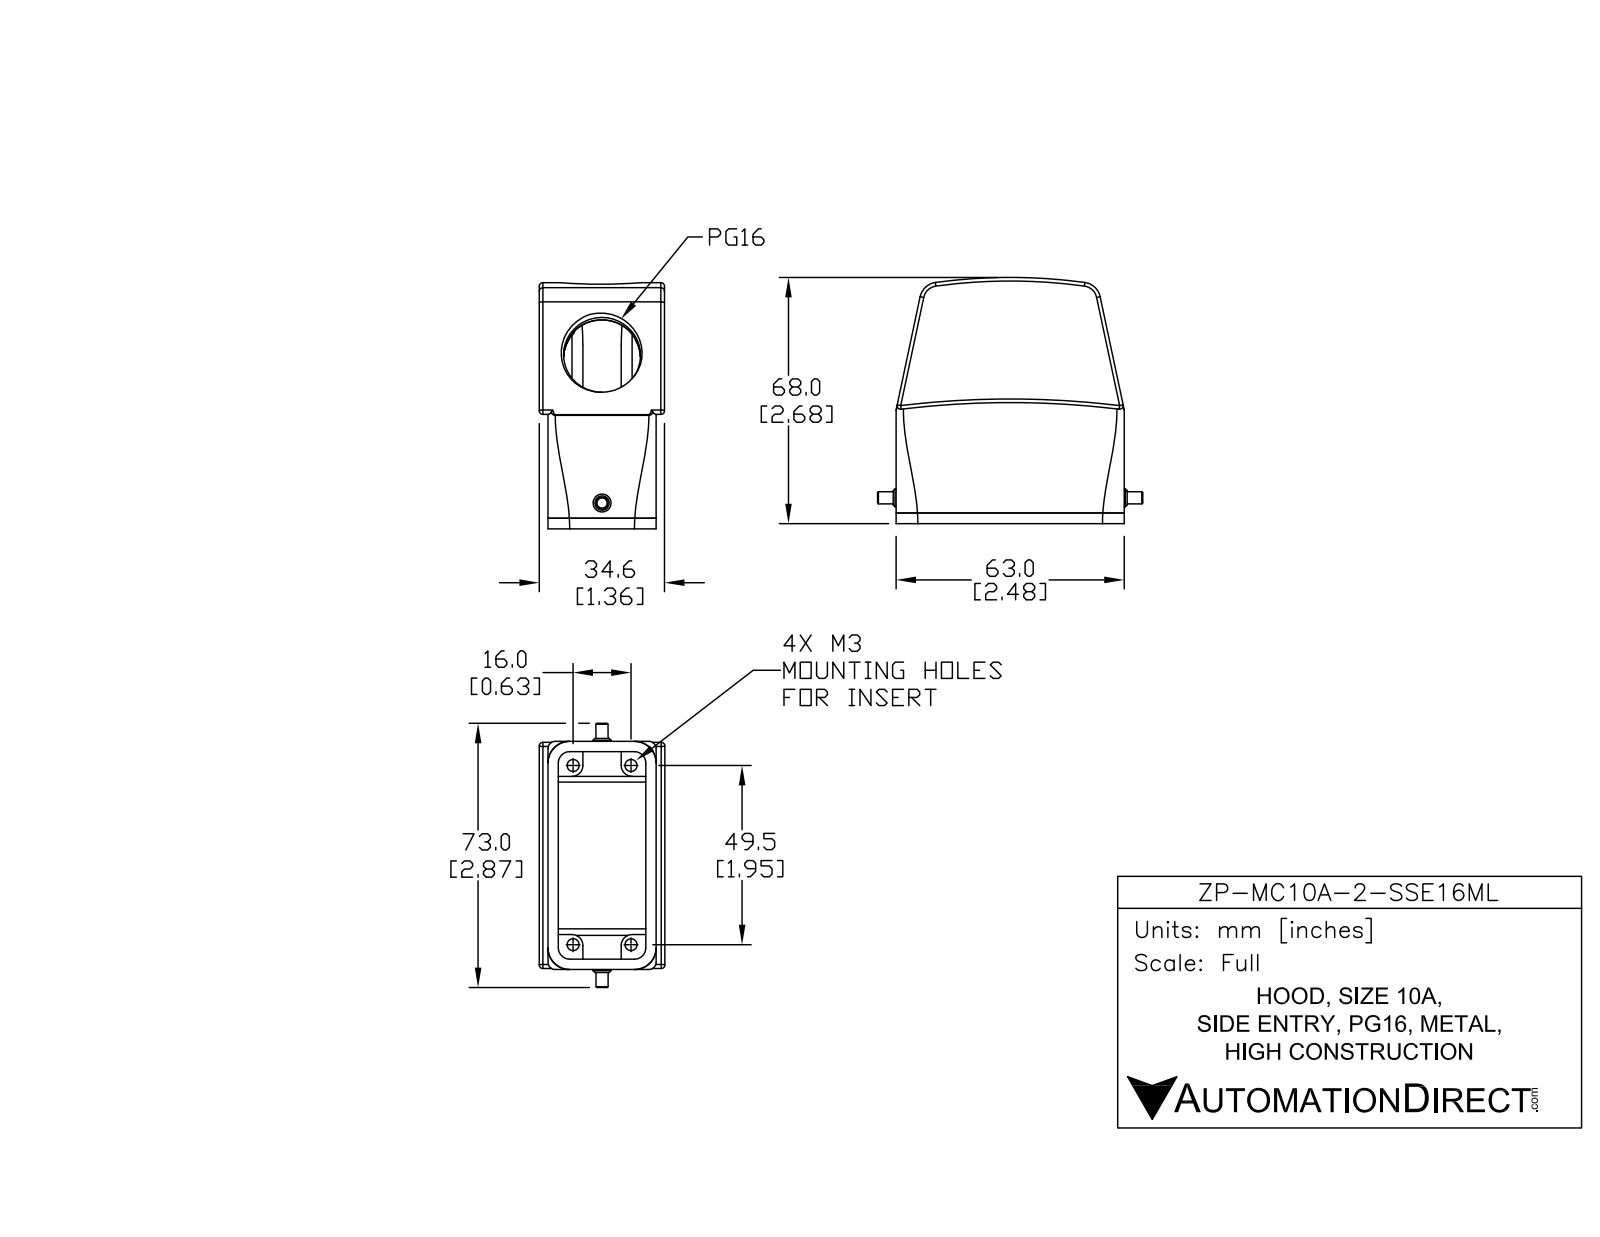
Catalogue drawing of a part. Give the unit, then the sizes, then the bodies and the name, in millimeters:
Units: millimetres
Overall size (bounding box): 73.25 × 68 × 34.6
Round holes (diameter × count): ⌀3 ×4, ⌀21.25 ×1
Round bosses / shafts (diameter × count): ⌀4.95 ×1, ⌀3.33 ×1
Partial cylindrical surfaces — rounded edges, fillets, slot ends (radius × count): R1 ×9, R3 ×4, R2.15 ×2, R5 ×2, R29.32 ×1, R150.6 ×1, R153.45 ×1, R161.93 ×1
Main face-to-face distances: 2.85, 26.93, 24.08, 2.41, 5.26, 29.34, 32.19, 29.78, 34.6, 9.75
Hole centre spacings: 16, 49.5, 52.02
Volume: 47 746 mm³ · Surface area: 26 776 mm²
Bodies: 2 solids, 180 faces (52 planar, 79 cylindrical, 49 other)
Part name (STEP PRODUCT): ZP-MC10A-2-SSE16ML
STEP written by: SolidWorks 2014 (AUTOMOTIVE_DESIGN)
